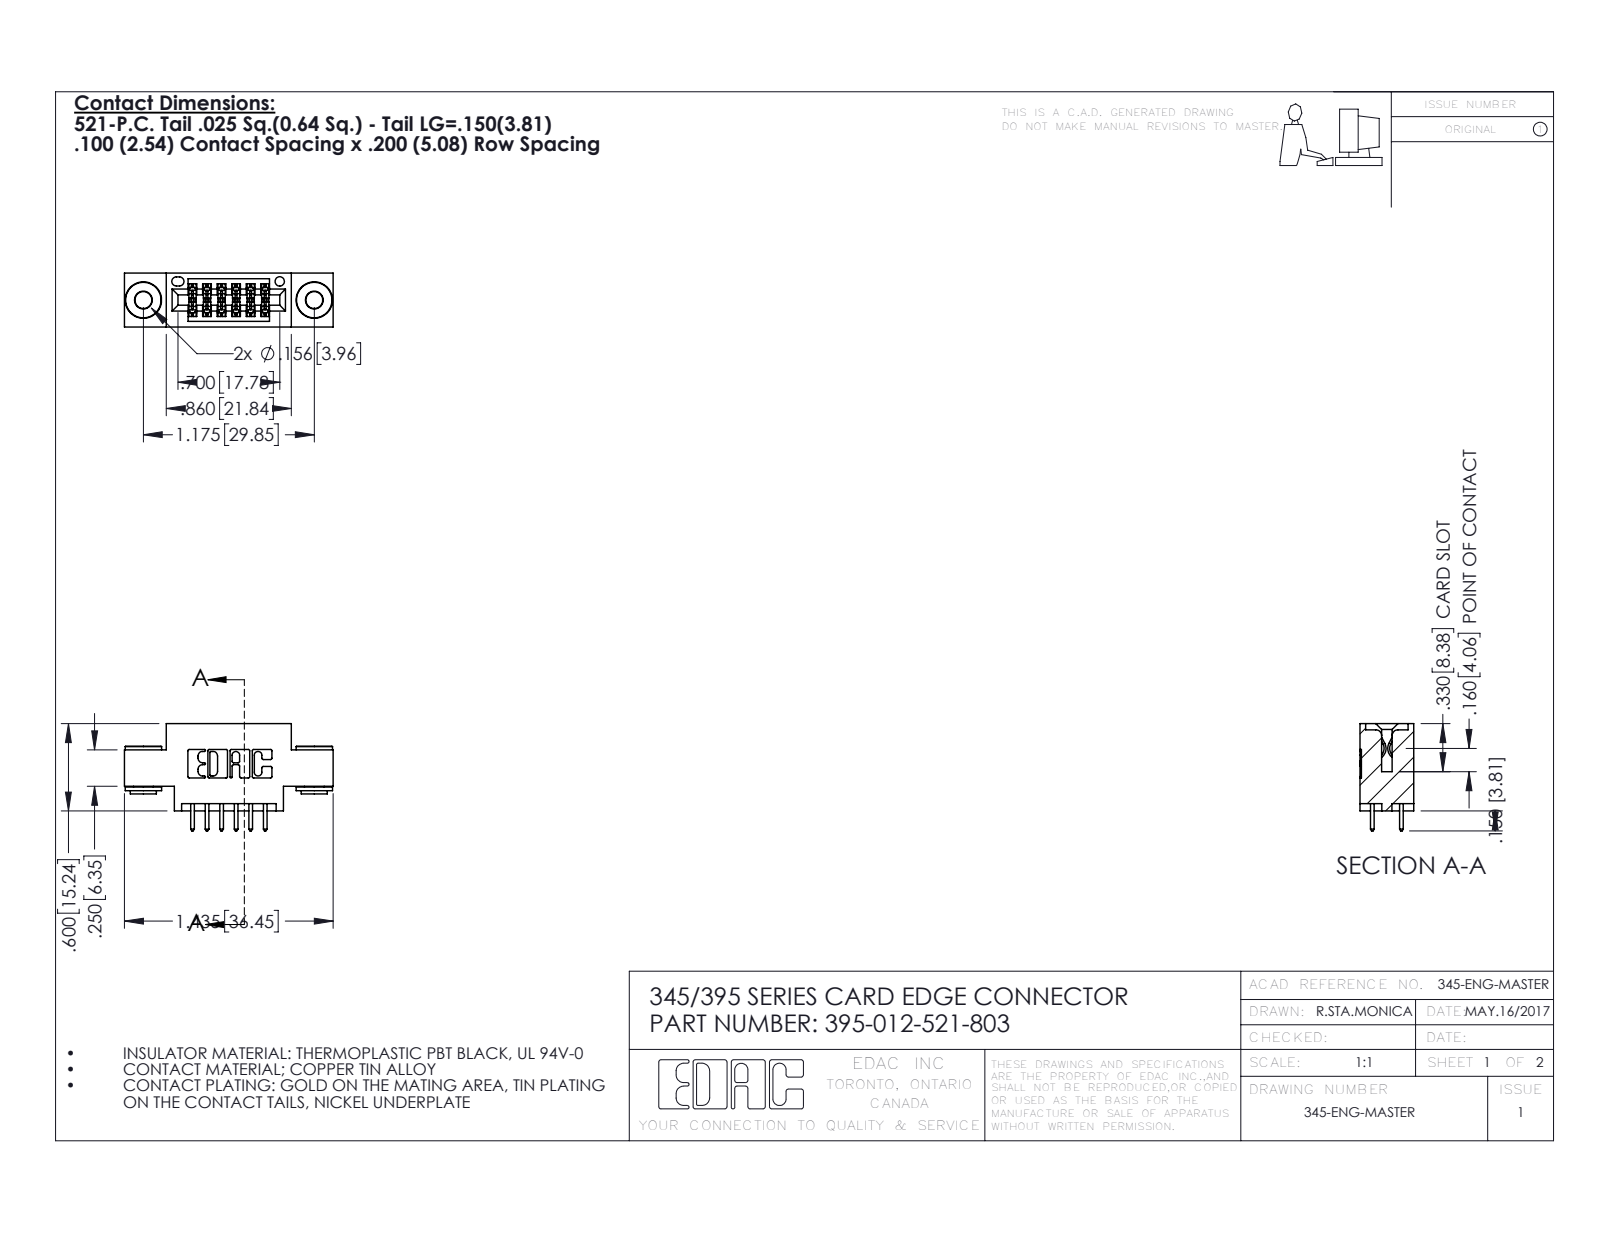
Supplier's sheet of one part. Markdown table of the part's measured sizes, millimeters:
| quantity | value |
| --- | --- |
| part name | 395-012-521-803; 345-250-002_345-250-002-102; 345 Part_0.170 Offset - 0.156 Dia-TH; 345-292-001_345-293-121 |
| STEP written by | SolidWorks 2016 (CONFIG_CONTROL_DESIGN) |
| units | millimeters |
| bodies | 15 solids, 768 faces (490 planar, 270 cylindrical, 8 other) |
| overall size | 36.4 × 18.7 × 9.4 |
| volume | 3 110 mm³ |
| surface area | 4 213 mm² |
| round holes (diameter × count) | 2.9 × 2, 4 × 2, 1.6 × 1 |
| round bosses / shafts (diameter × count) | 6.4 × 2, 4.6 × 2, 3.5 × 2 |
| partial cylindrical surfaces (radius × count) | 0.3 × 22, 0.2 × 18, 0.3 × 12, 0.2 × 6, 0.8 × 6, 0.7 × 3, 0.4 × 2, 0.5 × 2 |
| main face-to-face distances | 9.4, 5.1, 1.8, 7.6, 2.5, 0.6, 2.5, 6.9, 6.4, 5.7 |
| hole center spacings | 6.9, 24, 29.8 |
